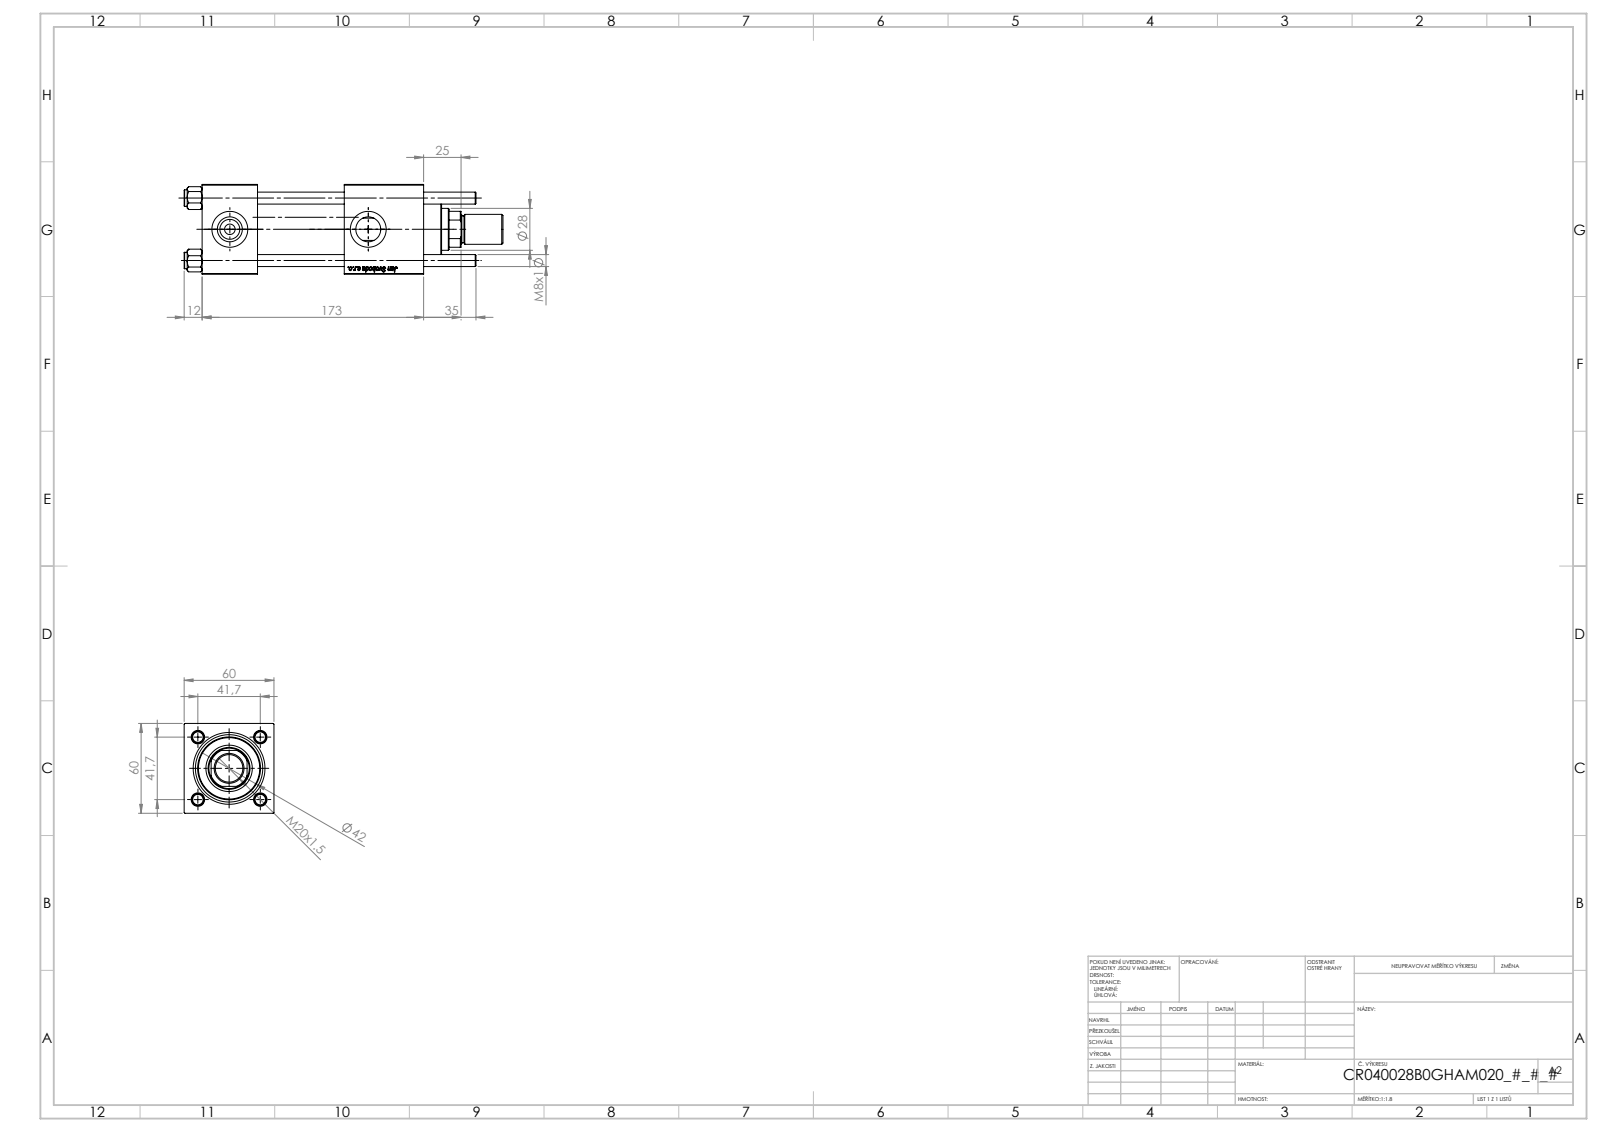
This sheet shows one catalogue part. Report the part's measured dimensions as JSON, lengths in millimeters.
{"part_name": "ROD_END_AH; V215CR_B-1; V215_VC_A; NUT_M5_B (+2 more)", "step_written_by": "SolidWorks 2019 (CONFIG_CONTROL_DESIGN)", "units": "millimeters", "bodies": {"solids": 12, "faces": 1173, "planar": 437, "cylindrical": 82, "other": 654}, "overall_size": [213, 60, 60], "volume_mm3": 444227, "surface_area_mm2": 122290, "round_holes": [[8, 4], [7, 2], [16.66, 2], [24, 2], [18.5, 1], [28, 1], [31, 1], [40, 1], [45, 1]], "round_bosses_or_shafts": [[11, 4], [46, 1], [42, 1], [20, 1], [18, 1]], "partial_cylinders_radius": [[13.5, 1]], "face_to_face_distances": [60, 37, 58, 95, 53, 119.3, 82.3, 24.3, 148, 111], "hole_center_spacings": [29.49, 41.7, 58.97, 92.5]}
